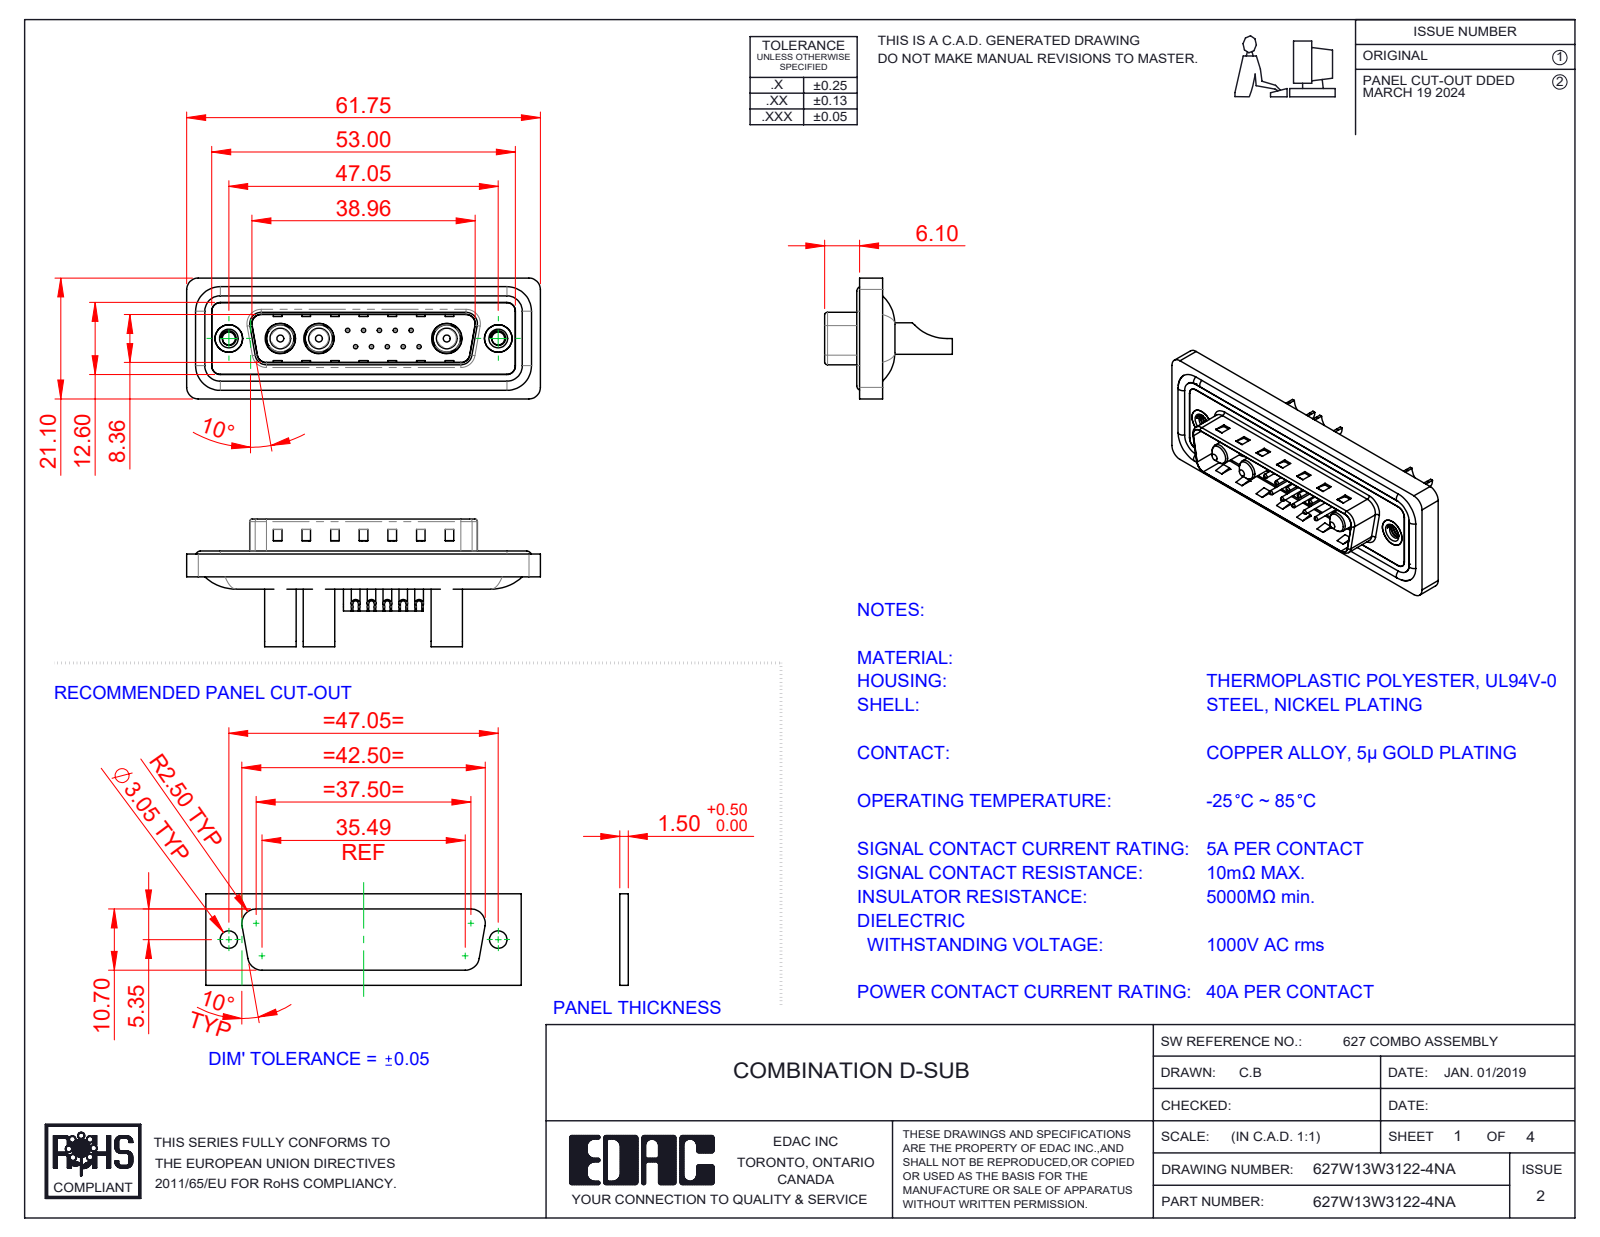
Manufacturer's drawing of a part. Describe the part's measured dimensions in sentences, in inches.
The part is named "627Combo Contact Row 2_22; 627Combo Contact Row 1_22; 627Combo Shell Rear_25 Contacts; 627Combo Waterproof Housing_25 Contacts (+5 more)". Its 3-D file was written by "SolidWorks 2023 (CONFIG_CONTROL_DESIGN)". It is 23 solids with 977 faces: 335 planar, 410 cylindrical and 232 other. Overall it measures 2.431 by 0.878 by 0.831 inches. Its volume is 0.456 cubic inches and its surface area 19.18 square inches. Round holes: 10 of diameter 0.03, 10 of diameter 0.039, 10 of diameter 0.063, 10 of diameter 0.079, 3 of diameter 0.181, 3 of diameter 0.191, 3 of diameter 0.209, 2 of diameter 0.089, 2 of diameter 0.157, 2 of diameter 0.189, 2 of diameter 0.197. Round bosses or shafts: 10 of diameter 0.059, 4 of diameter 0.063, 3 of diameter 0.217, 3 of diameter 0.205, 3 of diameter 0.187, 3 of diameter 0.148, 3 of diameter 0.142, 2 of diameter 0.193. Partial cylindrical surfaces (rounded edges, fillets, slot ends): 22 of radius 0.059, 18 of radius 0.079, 8 of radius 0.02, 8 of radius 0.063, 6 of radius 0.039, 4 of radius 0.01, 4 of radius 0.024, 4 of radius 0.026. The main face-to-face distances are 0.016, 0.043, 0.059, 0.063, 0.02, 0.122, 0.114, 0.032, 0.377, 0.161. The hole center spacings are 0.124, 0.109, 0.198, 0.218, 0.295, 0.198, 0.327, 0.398.
